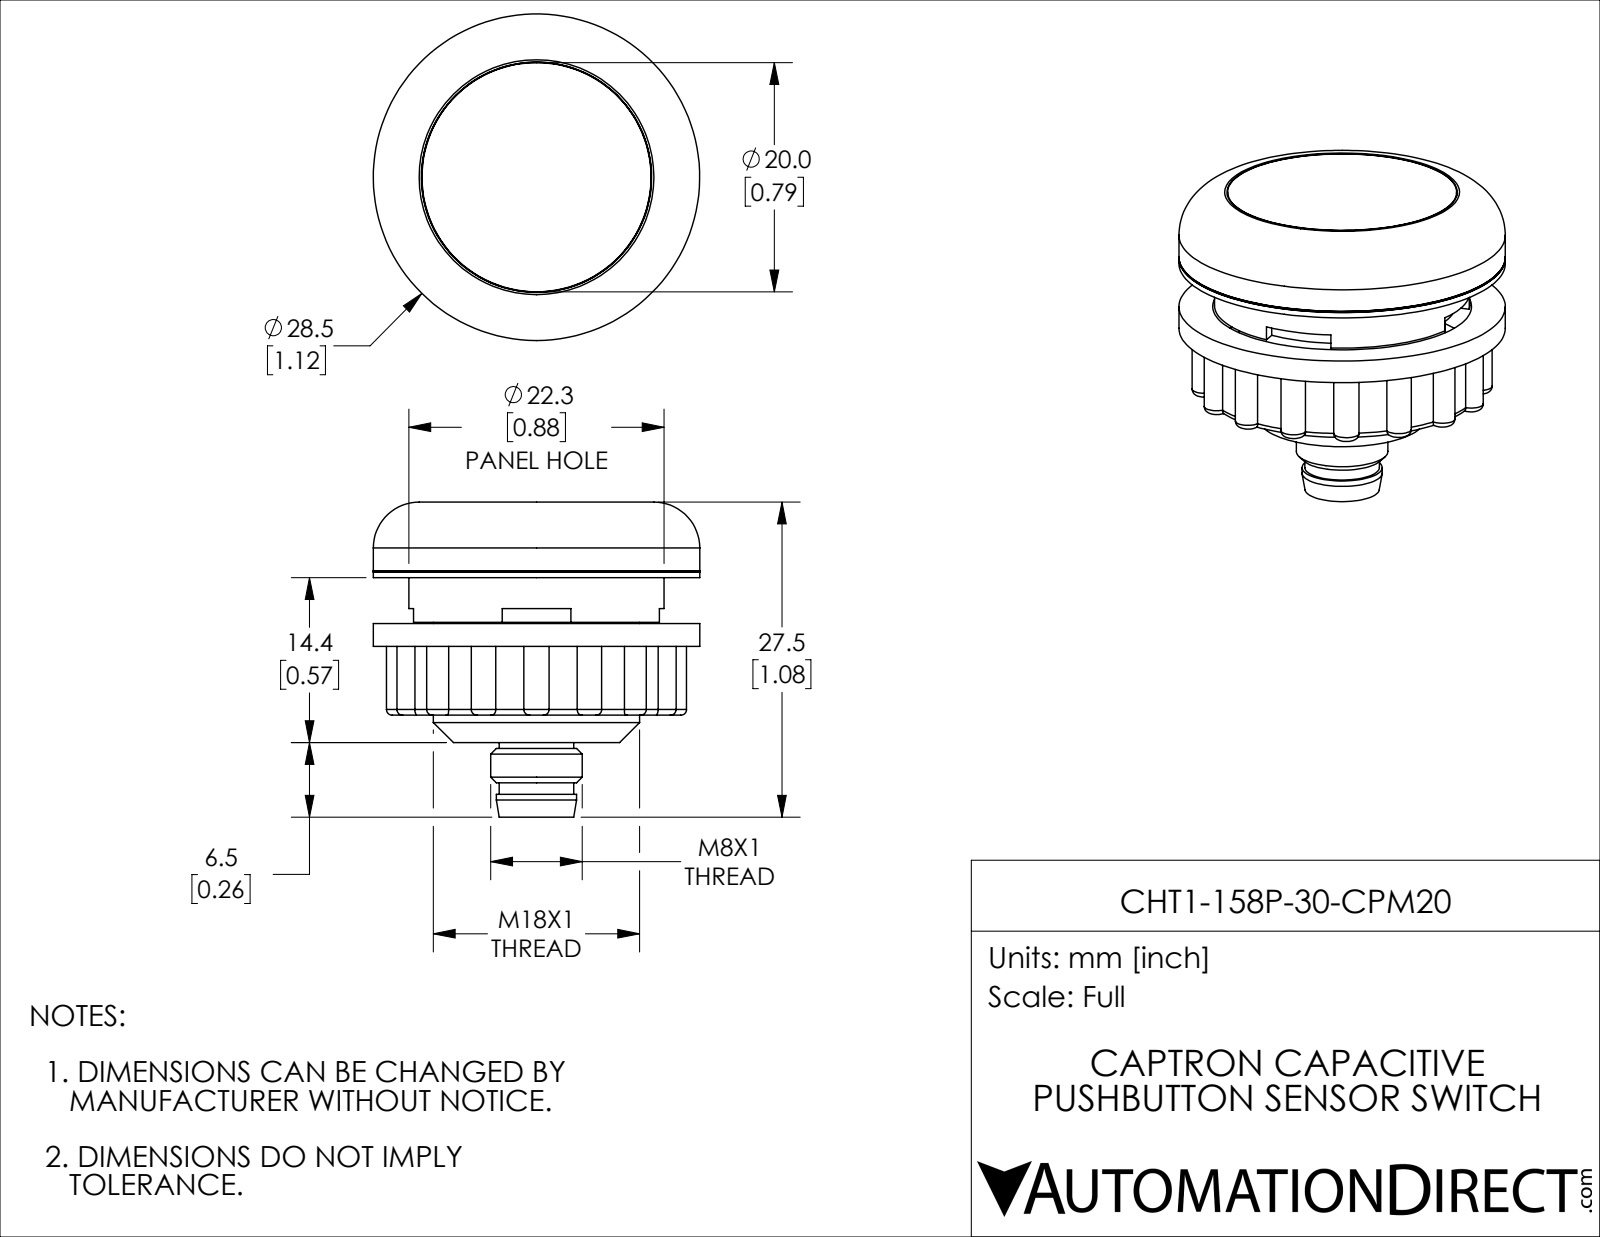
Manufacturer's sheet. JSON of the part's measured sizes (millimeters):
{"part_name": "CHT1-158P-30-CPM20", "step_written_by": "SolidWorks 2019 (CONFIG_CONTROL_DESIGN)", "units": "millimeters", "bodies": {"solids": 11, "faces": 213, "planar": 41, "cylindrical": 97, "other": 75}, "overall_size": [28.5, 28.5, 27.5], "volume_mm3": 9654, "surface_area_mm2": 8353, "round_holes": [[2, 2], [6, 1], [17, 1], [20.1, 1], [22.6, 1]], "round_bosses_or_shafts": [[1, 4], [28.5, 1], [22.28, 1], [19.08, 1], [18, 1], [8, 1], [7, 1], [6.5, 1]], "partial_cylinders_radius": [[1.1, 16], [9.9, 1], [12, 1]], "face_to_face_distances": [6, 3, 3.1, 0.5, 4, 6.6, 4.5, 6.1, 2, 8], "hole_center_spacings": [5.5, 11]}
